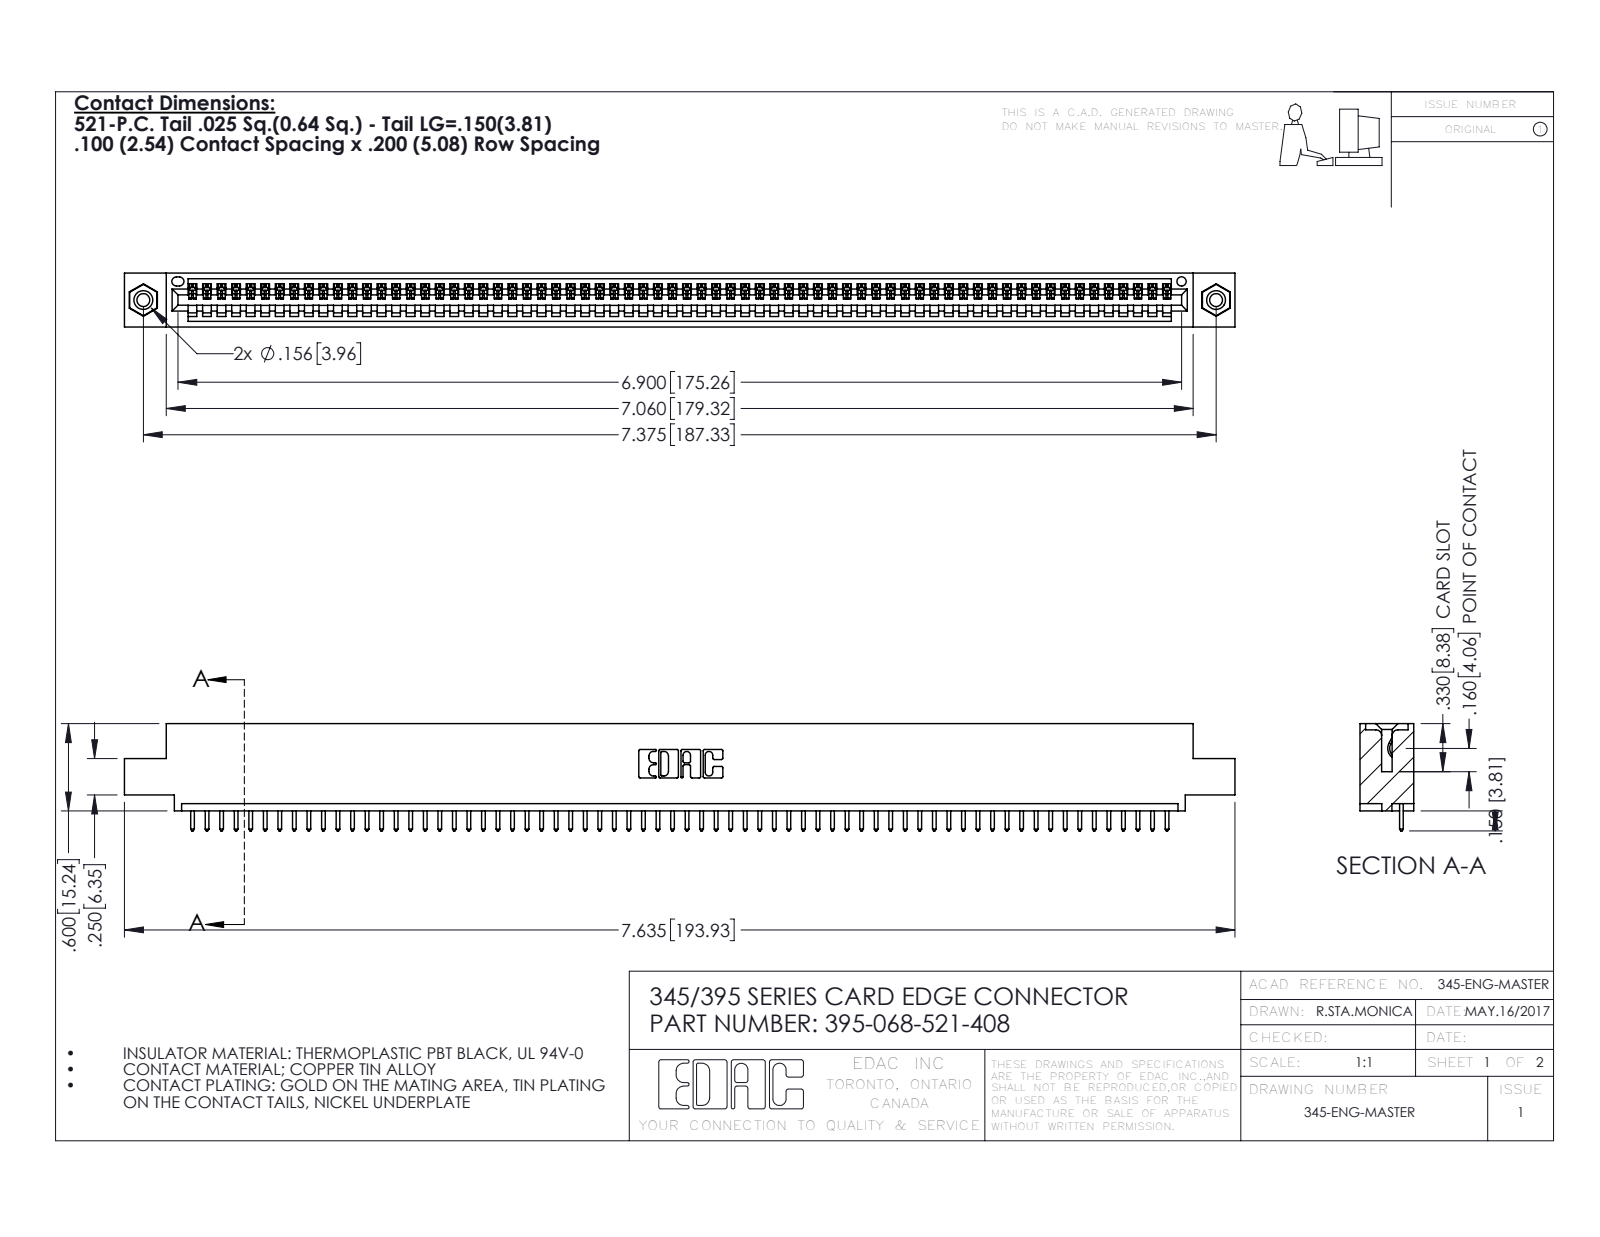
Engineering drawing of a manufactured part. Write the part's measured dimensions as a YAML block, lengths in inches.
part_name: "345-250-001_345-250-003-102; 345-292-001_345-293-121; 395-068-521-408; 345 Part_0.110 Offset - 0.156 Dia-TI"
step_written_by: "SolidWorks 2016 (CONFIG_CONTROL_DESIGN)"
units: inches
bodies: {solids: 71, faces: 4134, planar: 2836, cylindrical: 1282, other: 16}
overall_size: [7.635, 0.737, 0.37]
volume: 1.12
surface_area: 37.35
round_holes:
  - {diameter: 0.089, count: 2}
  - {diameter: 0.125, count: 2}
  - {diameter: 0.156, count: 2}
  - {diameter: 0.064, count: 1}
round_bosses_or_shafts:
  - {diameter: 0.155, count: 2}
partial_cylinders:
  - {radius: 0.006, count: 136}
  - {radius: 0.01, count: 136}
  - {radius: 0.01, count: 22}
  - {radius: 0.007, count: 6}
  - {radius: 0.031, count: 6}
  - {radius: 0.026, count: 3}
  - {radius: 0.031, count: 2}
  - {radius: 0.04, count: 2}
face_to_face_distances: [0.072, 0.298, 0.37, 0.2, 0.098, 0.272, 0.025, 0.225, 0.149, 0.072]
hole_center_spacings: [0.27, 7.139, 7.375]
